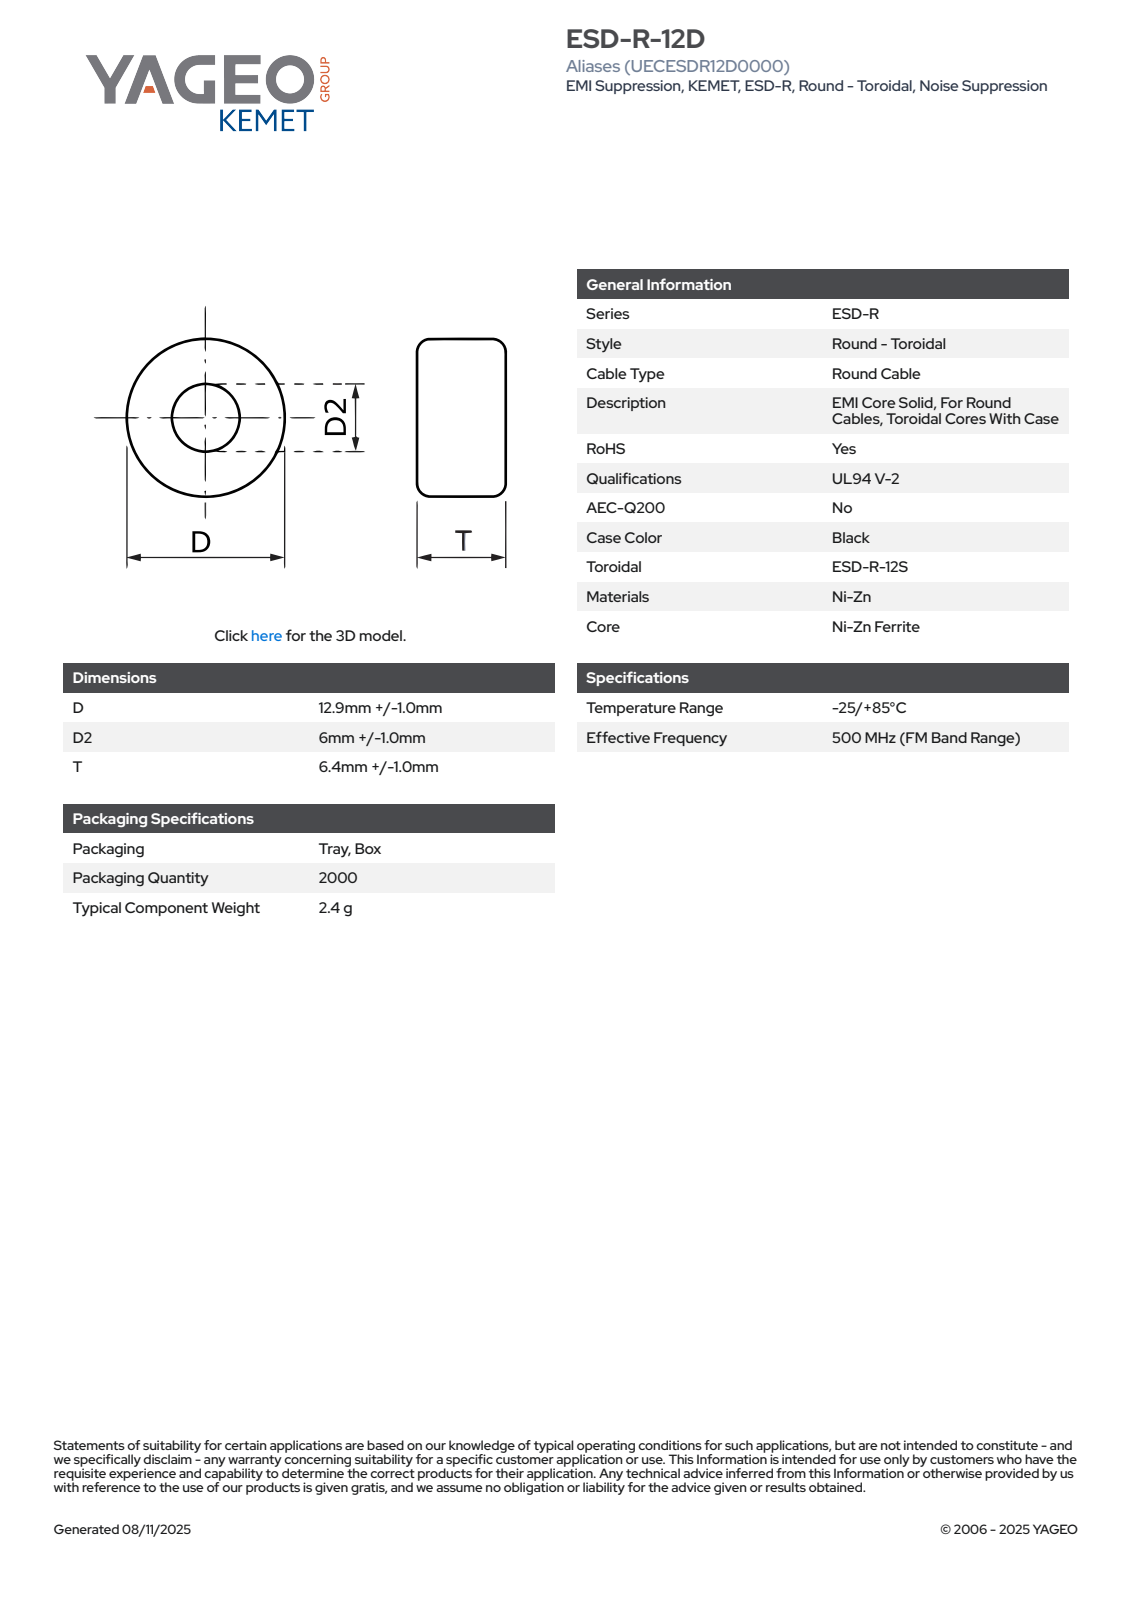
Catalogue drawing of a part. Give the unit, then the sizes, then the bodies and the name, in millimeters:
Units: millimetres
Overall size (bounding box): 13.91 × 13.9 × 7.4
Round holes (diameter × count): ⌀6 ×1
Round bosses / shafts (diameter × count): ⌀13.9 ×1
Partial cylindrical surfaces — rounded edges, fillets, slot ends (radius × count): R6.96 ×1
Main face-to-face distances: 7.4, 2.85, 4.55, 1.7, 0.32, 3.17, 4.23, 1.38, 1.06, 3.91
Volume: 910 mm³ · Surface area: 695 mm²
Bodies: 1 solid, 66 faces (24 planar, 7 cylindrical, 35 other)
Part name (STEP PRODUCT): EC_KBC_D13.9D26T7.4
STEP written by: SolidWorks 2021 (AUTOMOTIVE_DESIGN)
